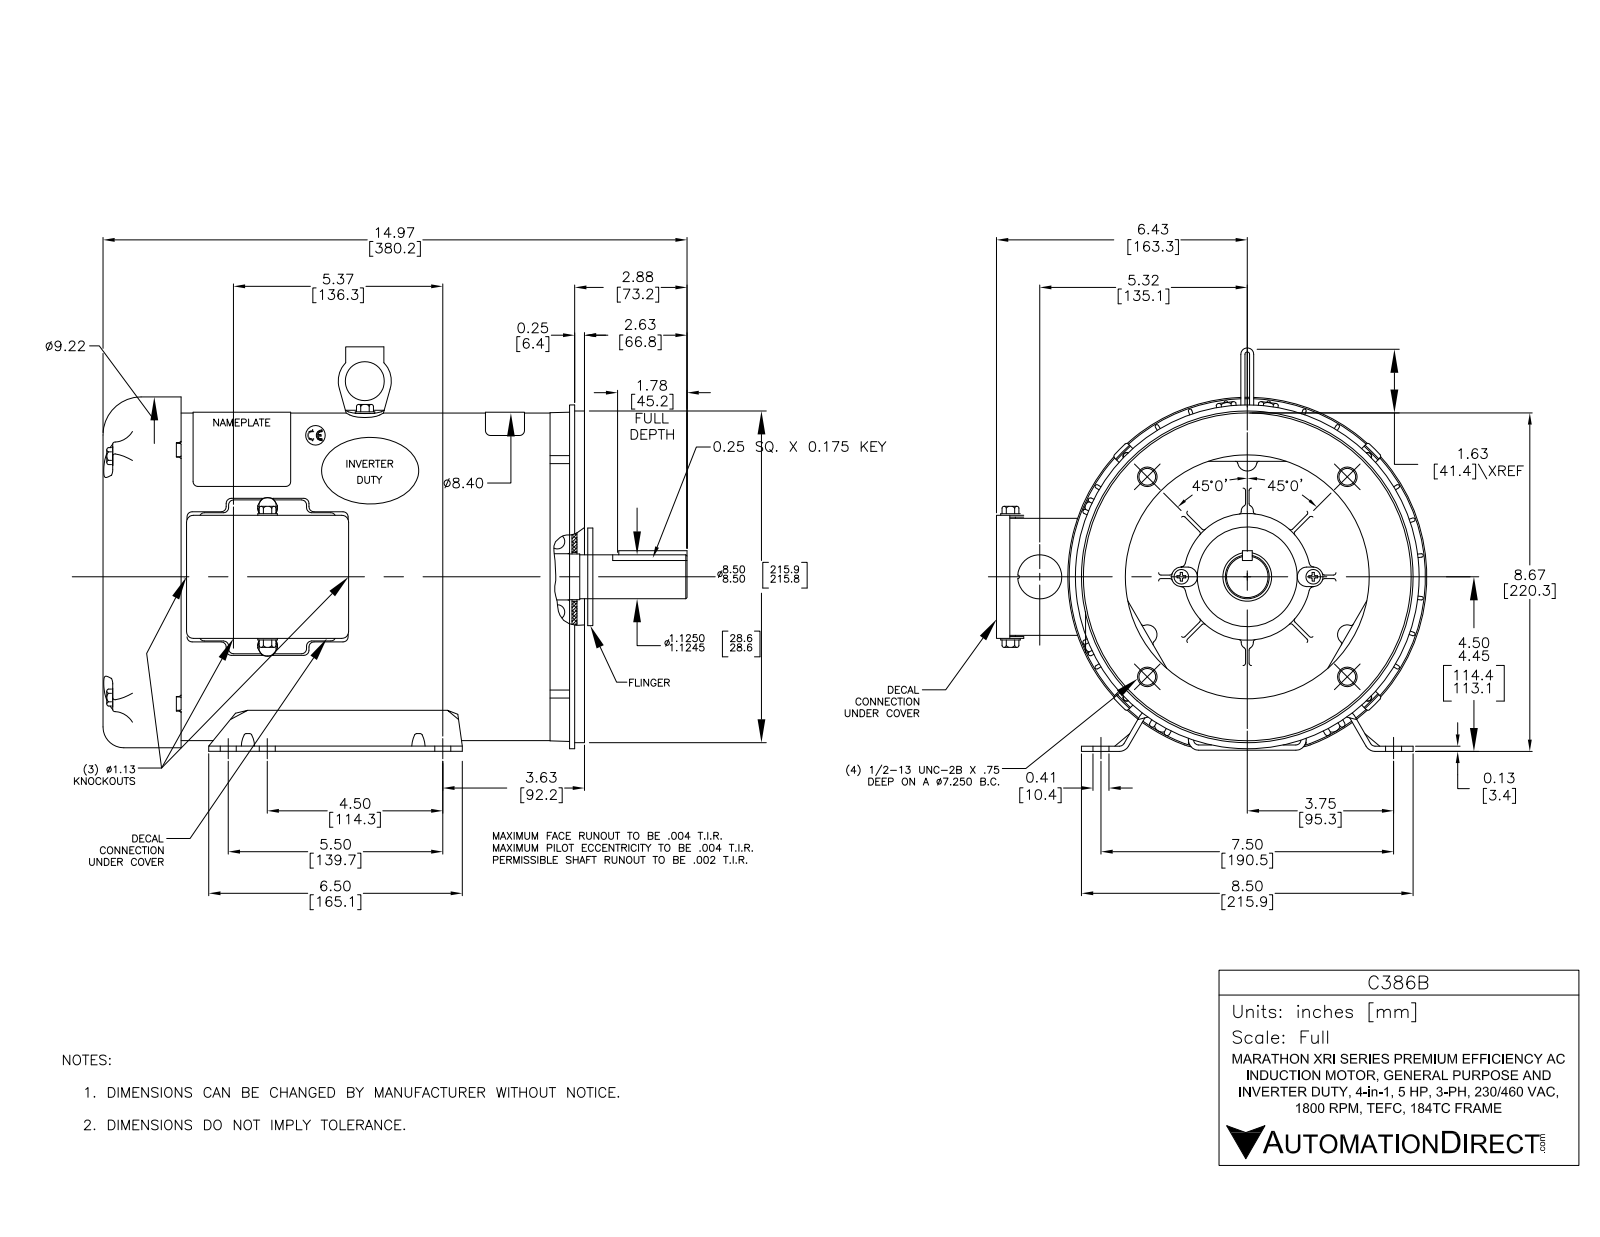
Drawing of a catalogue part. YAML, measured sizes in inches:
part_name: "C383B From G590 1st"
step_written_by: "SolidWorks 2017 (AUTOMOTIVE_DESIGN)"
units: inches
bodies: {solids: 29, faces: 3321, planar: 943, cylindrical: 968, other: 1410}
overall_size: [14.963, 11.326, 10.364]
volume: 138
surface_area: 1510
round_holes:
  - {diameter: 0.38, count: 8}
  - {diameter: 0.213, count: 7}
  - {diameter: 0.43, count: 6}
  - {diameter: 0.153, count: 4}
  - {diameter: 0.201, count: 4}
  - {diameter: 0.218, count: 4}
  - {diameter: 0.28, count: 4}
  - {diameter: 0.421, count: 4}
  - {diameter: 0.422, count: 4}
  - {diameter: 0.103, count: 2}
  - {diameter: 0.206, count: 2}
  - {diameter: 0.5, count: 2}
round_bosses_or_shafts:
  - {diameter: 0.52, count: 10}
  - {diameter: 0.25, count: 10}
  - {diameter: 0.19, count: 6}
  - {diameter: 0.414, count: 4}
  - {diameter: 0.373, count: 2}
  - {diameter: 0.309, count: 2}
  - {diameter: 0.112, count: 2}
  - {diameter: 9.22, count: 1}
partial_cylinders:
  - {radius: 0.06, count: 90}
  - {radius: 0.095, count: 80}
  - {radius: 0.02, count: 62}
  - {radius: 0.045, count: 25}
  - {radius: 0.13, count: 24}
  - {radius: 0.03, count: 13}
  - {radius: 0.088, count: 8}
  - {radius: 0.264, count: 8}
face_to_face_distances: [1, 0.048, 0.035, 1.933, 0.933, 1.968, 0.968, 10.375, 11.375, 12.307]
hole_center_spacings: [1.5, 2.88, 3.091, 3.191, 3.855, 4.567, 4.89, 5.682]
